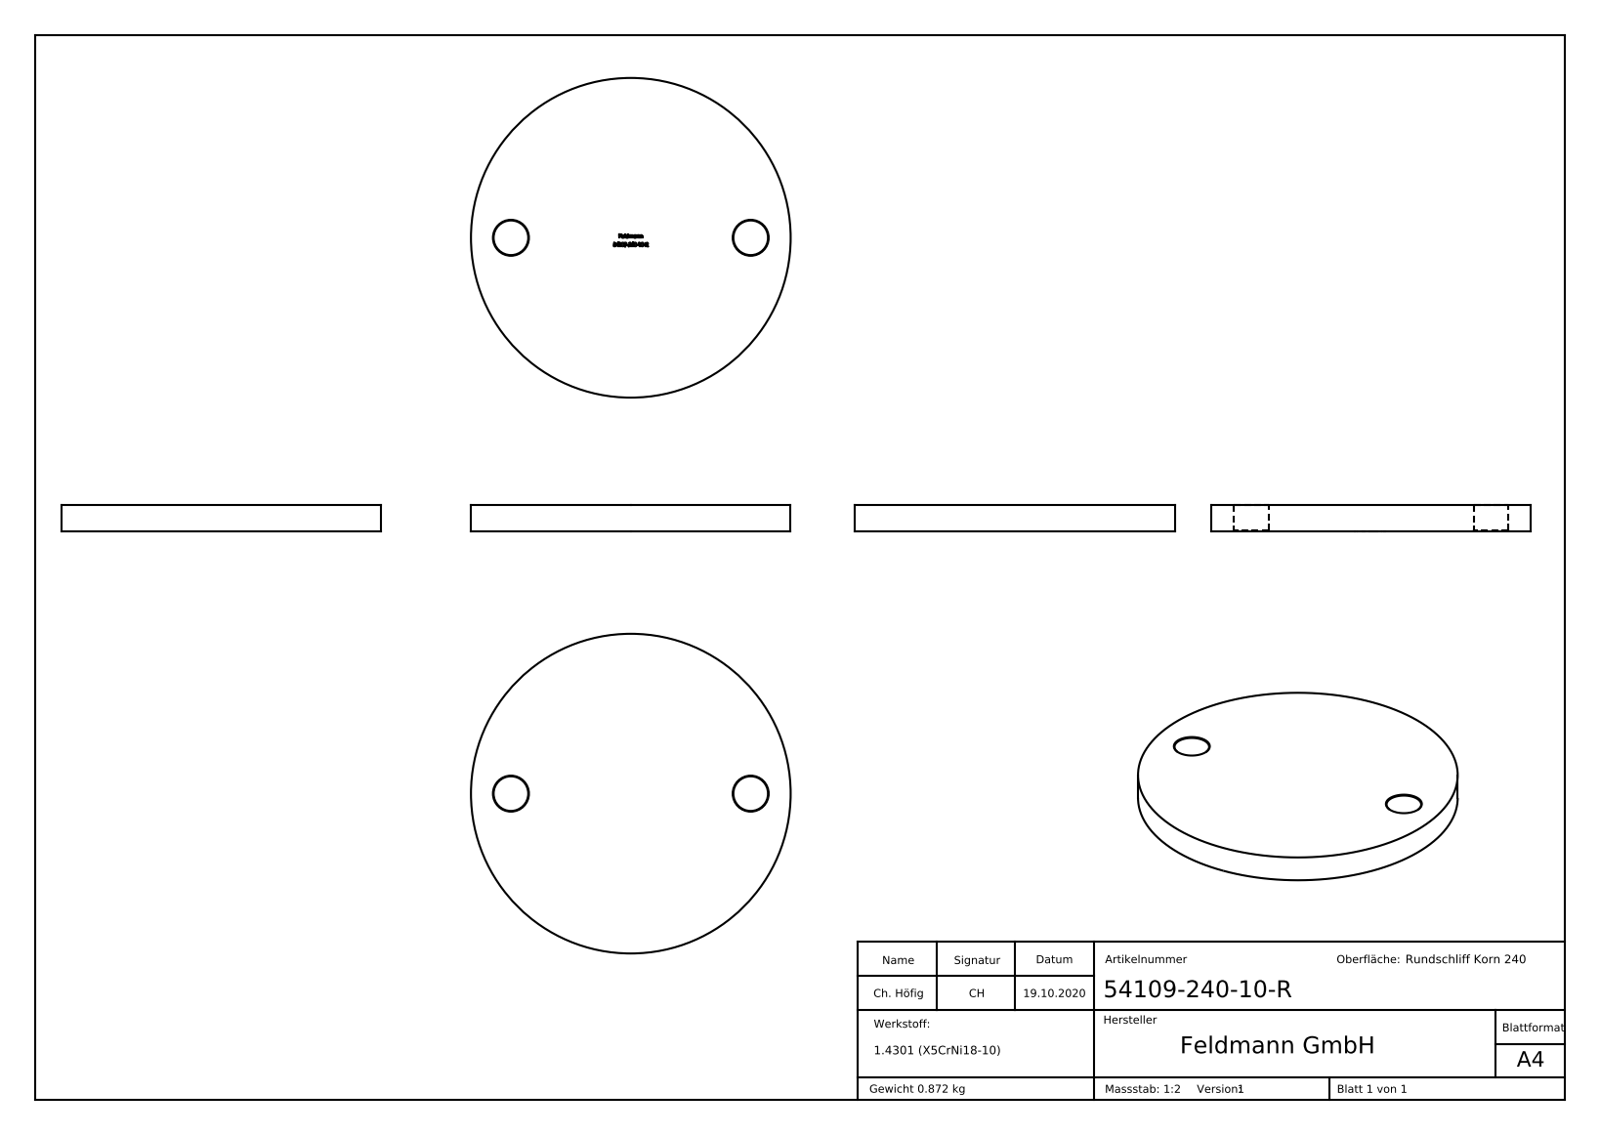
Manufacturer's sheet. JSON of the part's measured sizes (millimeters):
{"part_name": "54109-240-10-R", "step_written_by": "SolidWorks 2018 (CONFIG_CONTROL_DESIGN)", "units": "millimeters", "bodies": {"solids": 1, "faces": 281, "planar": 164, "cylindrical": 6, "other": 111}, "overall_size": [120, 120, 10], "volume_mm3": 110437, "surface_area_mm2": 26663, "round_holes": [[13, 2]], "round_bosses_or_shafts": [[120, 1]], "face_to_face_distances": [10, 9.9, 7.54, 4.9, 4.78, 0.58, 3.19, 7.33, 0.75, 2.97], "hole_center_spacings": [90]}
